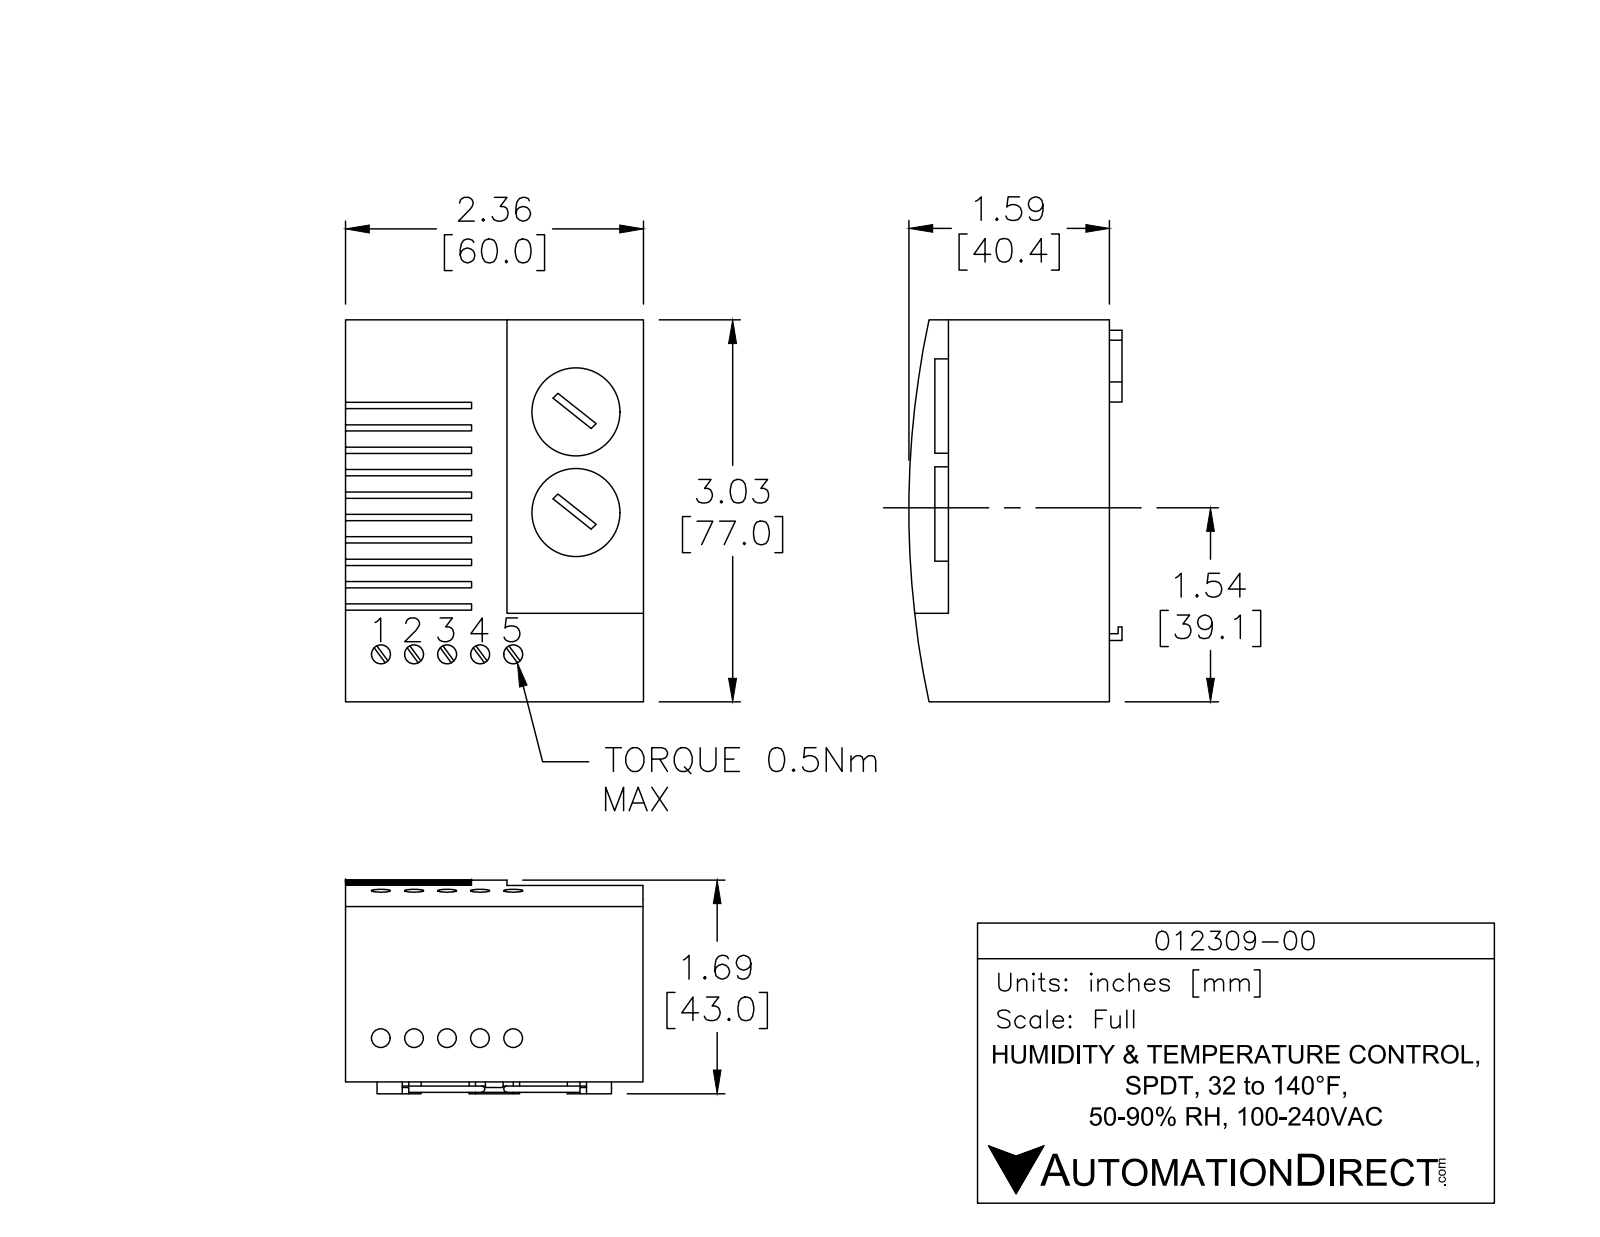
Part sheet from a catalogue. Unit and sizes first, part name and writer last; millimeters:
Units: millimetres
Overall size (bounding box): 78.6 × 59.9 × 42.8
Round holes (diameter × count): ⌀3.8 ×10, ⌀14.9 ×2
Partial cylindrical surfaces — rounded edges, fillets, slot ends (radius × count): R0.8 ×36, R1.5 ×12, R0.6 ×3, R0.5 ×1, R0.5 ×1, R5.1 ×1, R184.2 ×1, R196.2 ×1
Main face-to-face distances: 3, 4.6, 1.5, 7.6, 59.9, 1.5, 6.1, 9.1, 12.2, 10.7
Hole centre spacings: 7.6, 15.2, 22.9, 30.5, 24.8, 28.3, 31.5, 36
Volume: 151 400 mm³ · Surface area: 32 500 mm²
Bodies: 1 solid, 282 faces (137 planar, 105 cylindrical, 40 other)
Part name (STEP PRODUCT): 012309-00
STEP written by: SolidWorks 2013 (AUTOMOTIVE_DESIGN)
